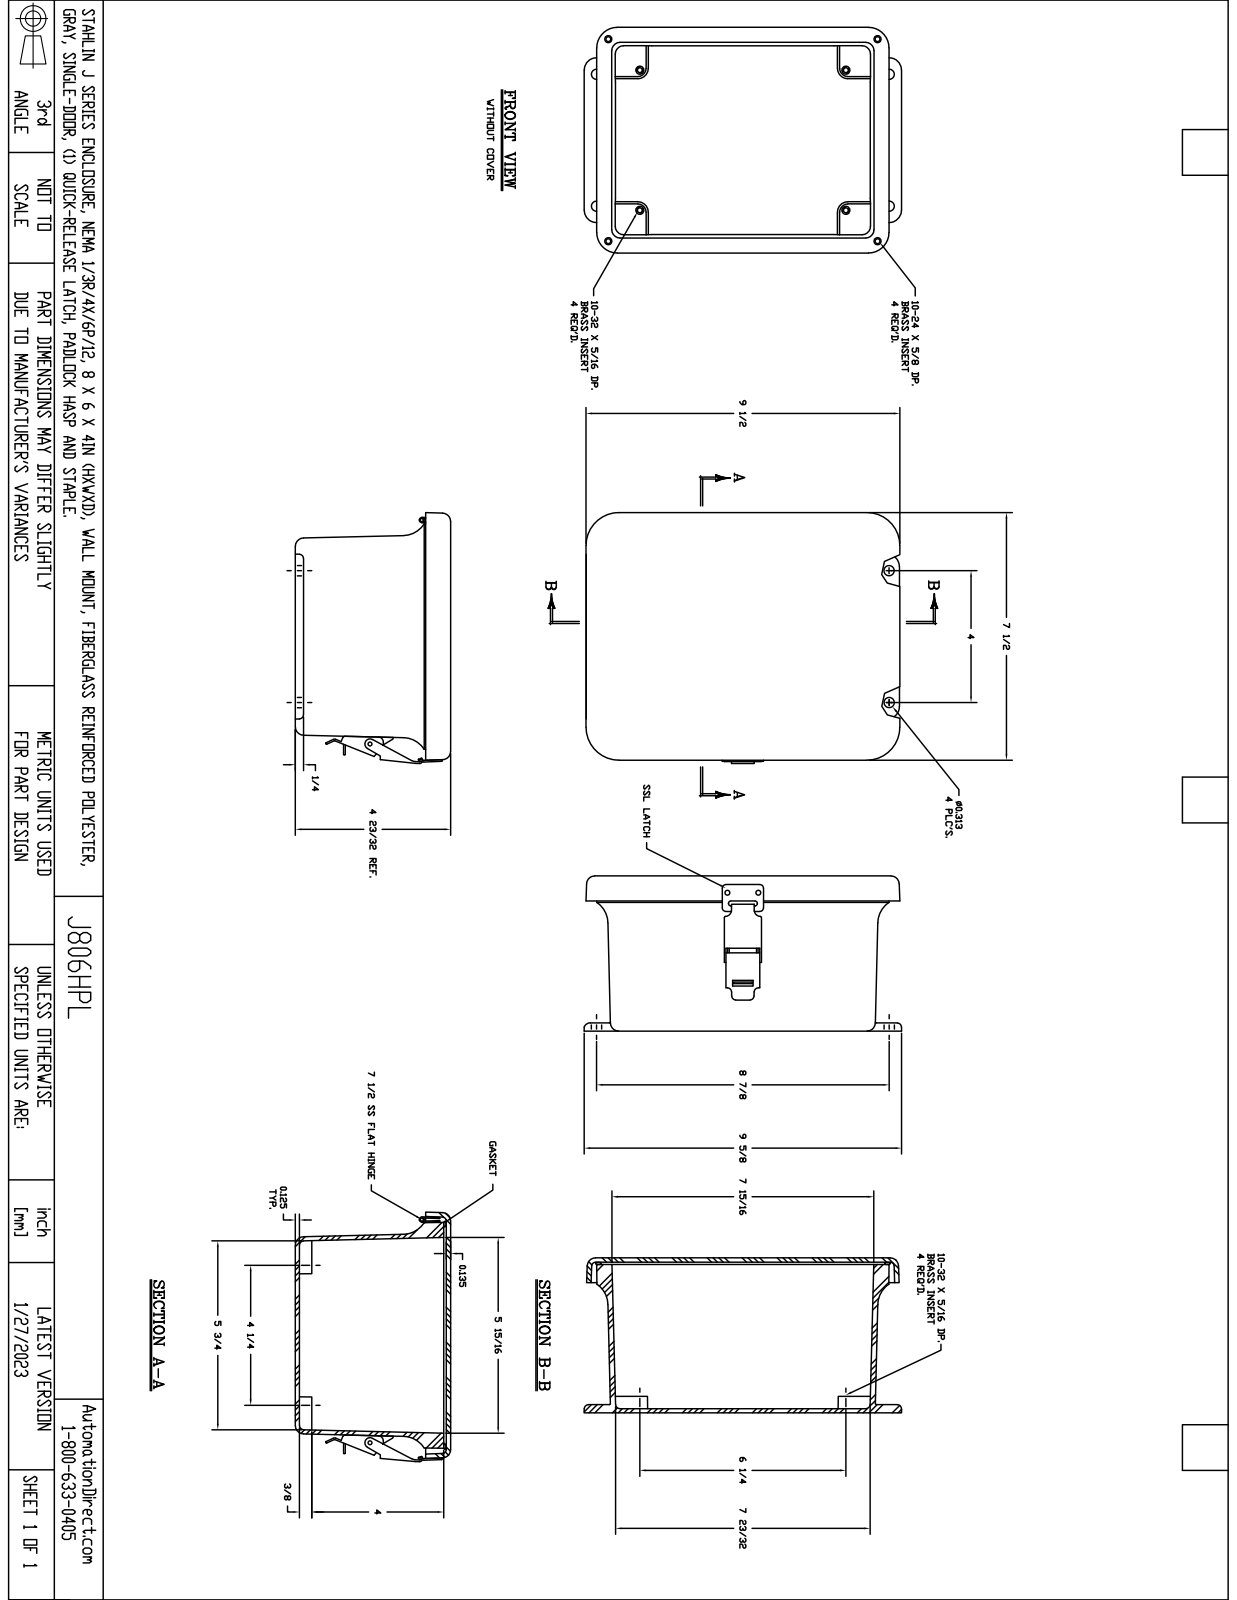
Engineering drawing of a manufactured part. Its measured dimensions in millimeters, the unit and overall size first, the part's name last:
Units: millimetres
Overall size (bounding box): 244.5 × 193.2 × 119.8
Round holes (diameter × count): ⌀3.6 ×12, ⌀3.3 ×6, ⌀3.9 ×5, ⌀2.6 ×4, ⌀4 ×4, ⌀5.5 ×4, ⌀3.3 ×2, ⌀3.4 ×2, ⌀2.2 ×1, ⌀2.2 ×1, ⌀3.4 ×1, ⌀9.5 ×1
Round bosses / shafts (diameter × count): ⌀6.4 ×6, ⌀3.2 ×6, ⌀6.9 ×4, ⌀3.2 ×4, ⌀7.6 ×1, ⌀4.3 ×1, ⌀3.9 ×1, ⌀3 ×1
Partial cylindrical surfaces — rounded edges, fillets, slot ends (radius × count): R0.8 ×20, R3.2 ×16, R0.4 ×12, R1.1 ×8, R6.4 ×8, R0.8 ×6, R0.6 ×4, R1.5 ×4
Main face-to-face distances: 3.2, 3.4, 116.3, 119.8, 3.2, 113.2, 116.6, 114.3, 111.1, 2
Hole centre spacings: 88.9, 19.1, 6.4, 23.8, 33.7, 133.9, 184.1, 225.1
Volume: 744 100 mm³ · Surface area: 399 100 mm²
Bodies: 26 solids, 676 faces (277 planar, 274 cylindrical, 125 other)
Part name (STEP PRODUCT): M806HPL
STEP written by: SolidWorks 2018 (AUTOMOTIVE_DESIGN)
